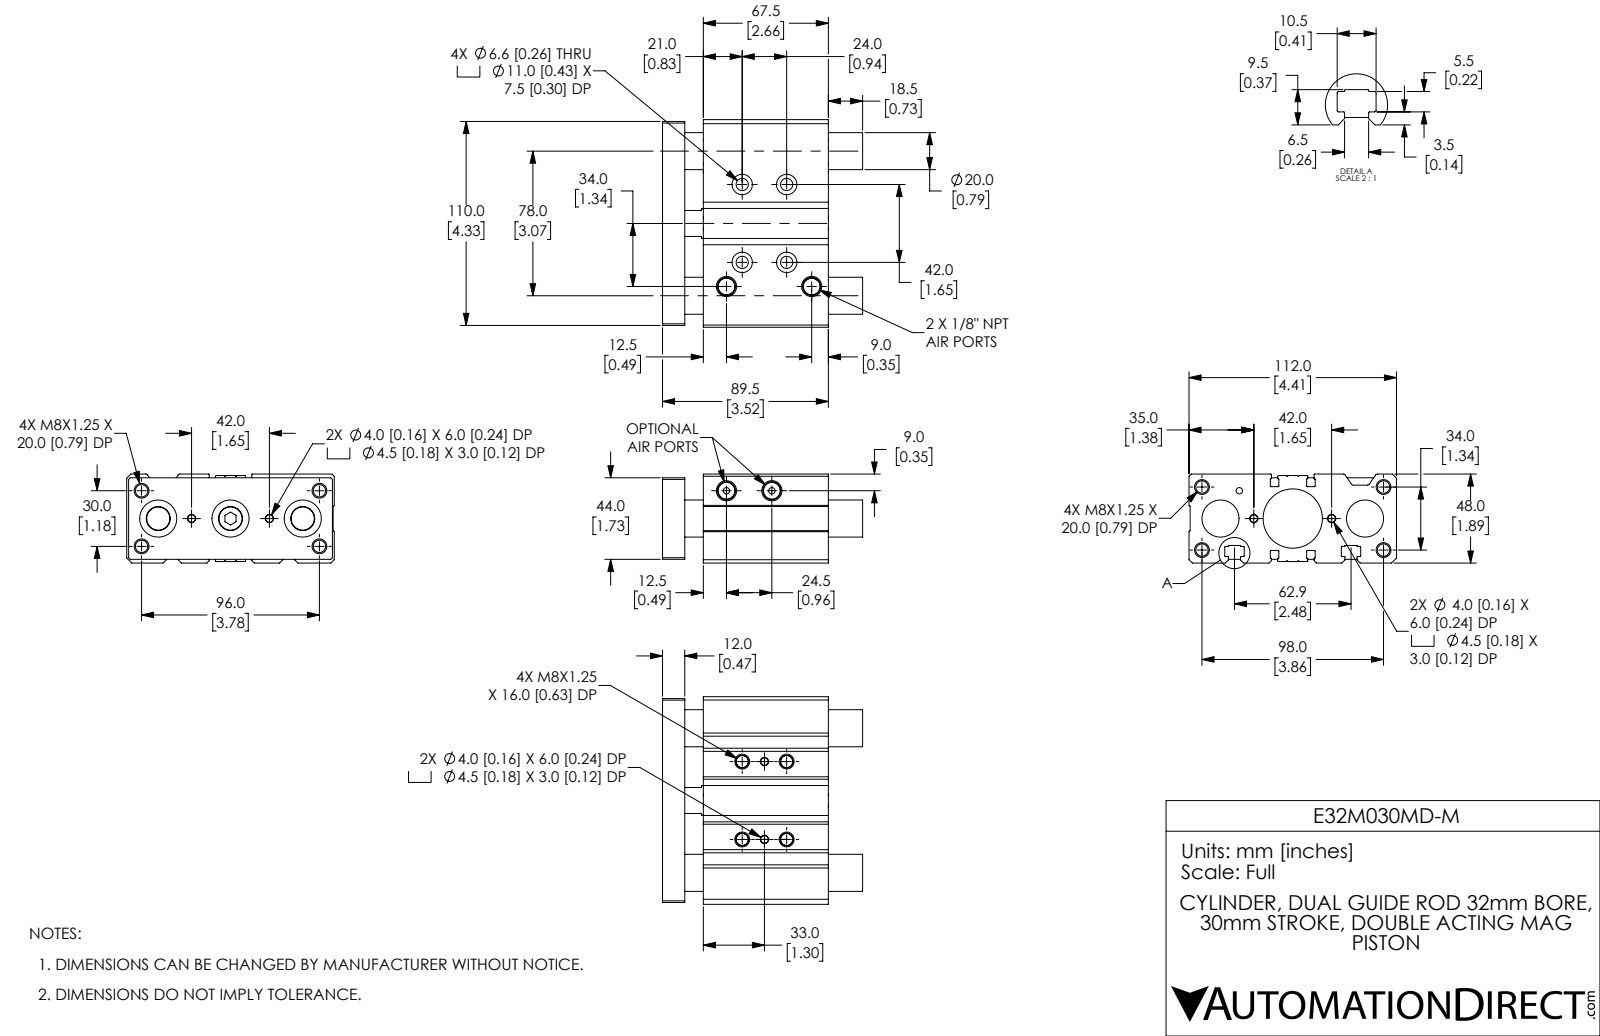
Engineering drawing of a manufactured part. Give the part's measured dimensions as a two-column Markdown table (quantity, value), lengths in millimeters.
| quantity | value |
| --- | --- |
| part name | E32M030MD-M_BODY; E32M030MD-M; E32M030MD-M_ENDPLATE |
| STEP written by | SolidWorks 2019 (CONFIG_CONTROL_DESIGN) |
| units | millimeters |
| bodies | 5 solids, 423 faces (139 planar, 190 cylindrical, 94 other) |
| overall size | 112 × 108 × 48 |
| volume | 374 053 mm³ |
| surface area | 98 321 mm² |
| round holes (diameter × count) | 6.65 × 12, 4 × 4, 4.5 × 4, 6.6 × 4, 11 × 4, 3.43 × 3, 10 × 3, 20 × 3, 12.95 × 2, 20 × 1, 32 × 1, 32 × 1 |
| round bosses / shafts (diameter × count) | 16 × 1, 12.95 × 1 |
| partial cylindrical surfaces (radius × count) | 0.2 × 32, 0.4 × 28, 1.2 × 4, 0.3 × 2 |
| main face-to-face distances | 67.5, 22, 48, 12, 10, 89.5, 77.5, 2, 6, 46 |
| hole center spacings | 2.24, 12, 17.49, 19.72, 30.89, 32.02, 32.76, 42 |
